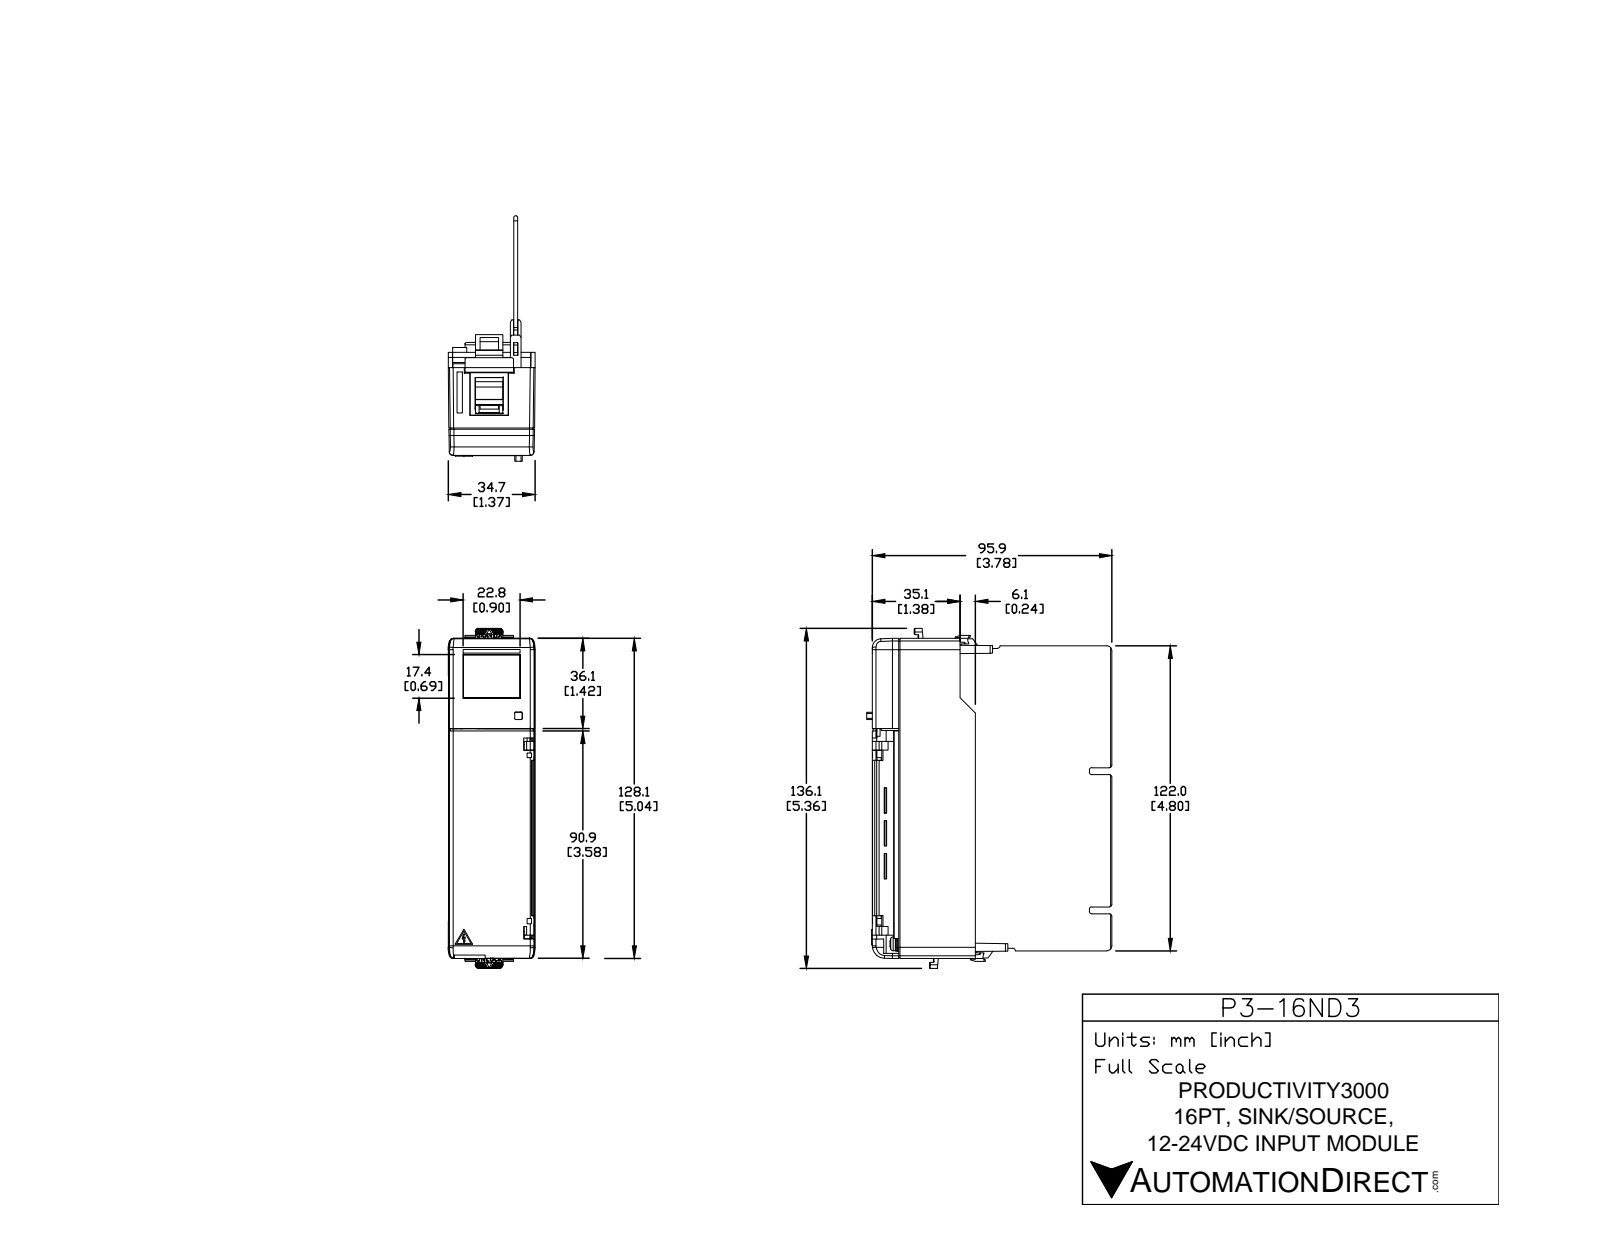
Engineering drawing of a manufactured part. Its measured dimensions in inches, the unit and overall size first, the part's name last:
Units: inches
Overall size (bounding box): 5.357 × 3.787 × 1.37
Round holes (diameter × count): ⌀0.126 ×22, ⌀0.197 ×2, ⌀0.071 ×1
Round bosses / shafts (diameter × count): ⌀0.217 ×22, ⌀0.118 ×22, ⌀0.094 ×20, ⌀0.22 ×2, ⌀0.087 ×2, ⌀0.079 ×2, ⌀0.059 ×1
Partial cylindrical surfaces — rounded edges, fillets, slot ends (radius × count): R0.02 ×91, R0.039 ×33, R0.012 ×29, R0.066 ×22, R0.059 ×13, R0.079 ×6, R0.008 ×5, R0.004 ×4
Main face-to-face distances: 0.063, 0.067, 1.111, 1.044, 1.282, 0.874, 0.087, 0.311, 0.268, 0.209
Hole centre spacings: 0.342, 0.3, 0.545, 0.6, 0.811, 0.9, 1.094, 1.2
Volume: 6.184 in³ · Surface area: 116.9 in²
Bodies: 1 solid, 3804 faces (2821 planar, 737 cylindrical, 246 other)
Part name (STEP PRODUCT): P3-16ND3
STEP written by: SolidWorks 2009 (CONFIG_CONTROL_DESIGN)
